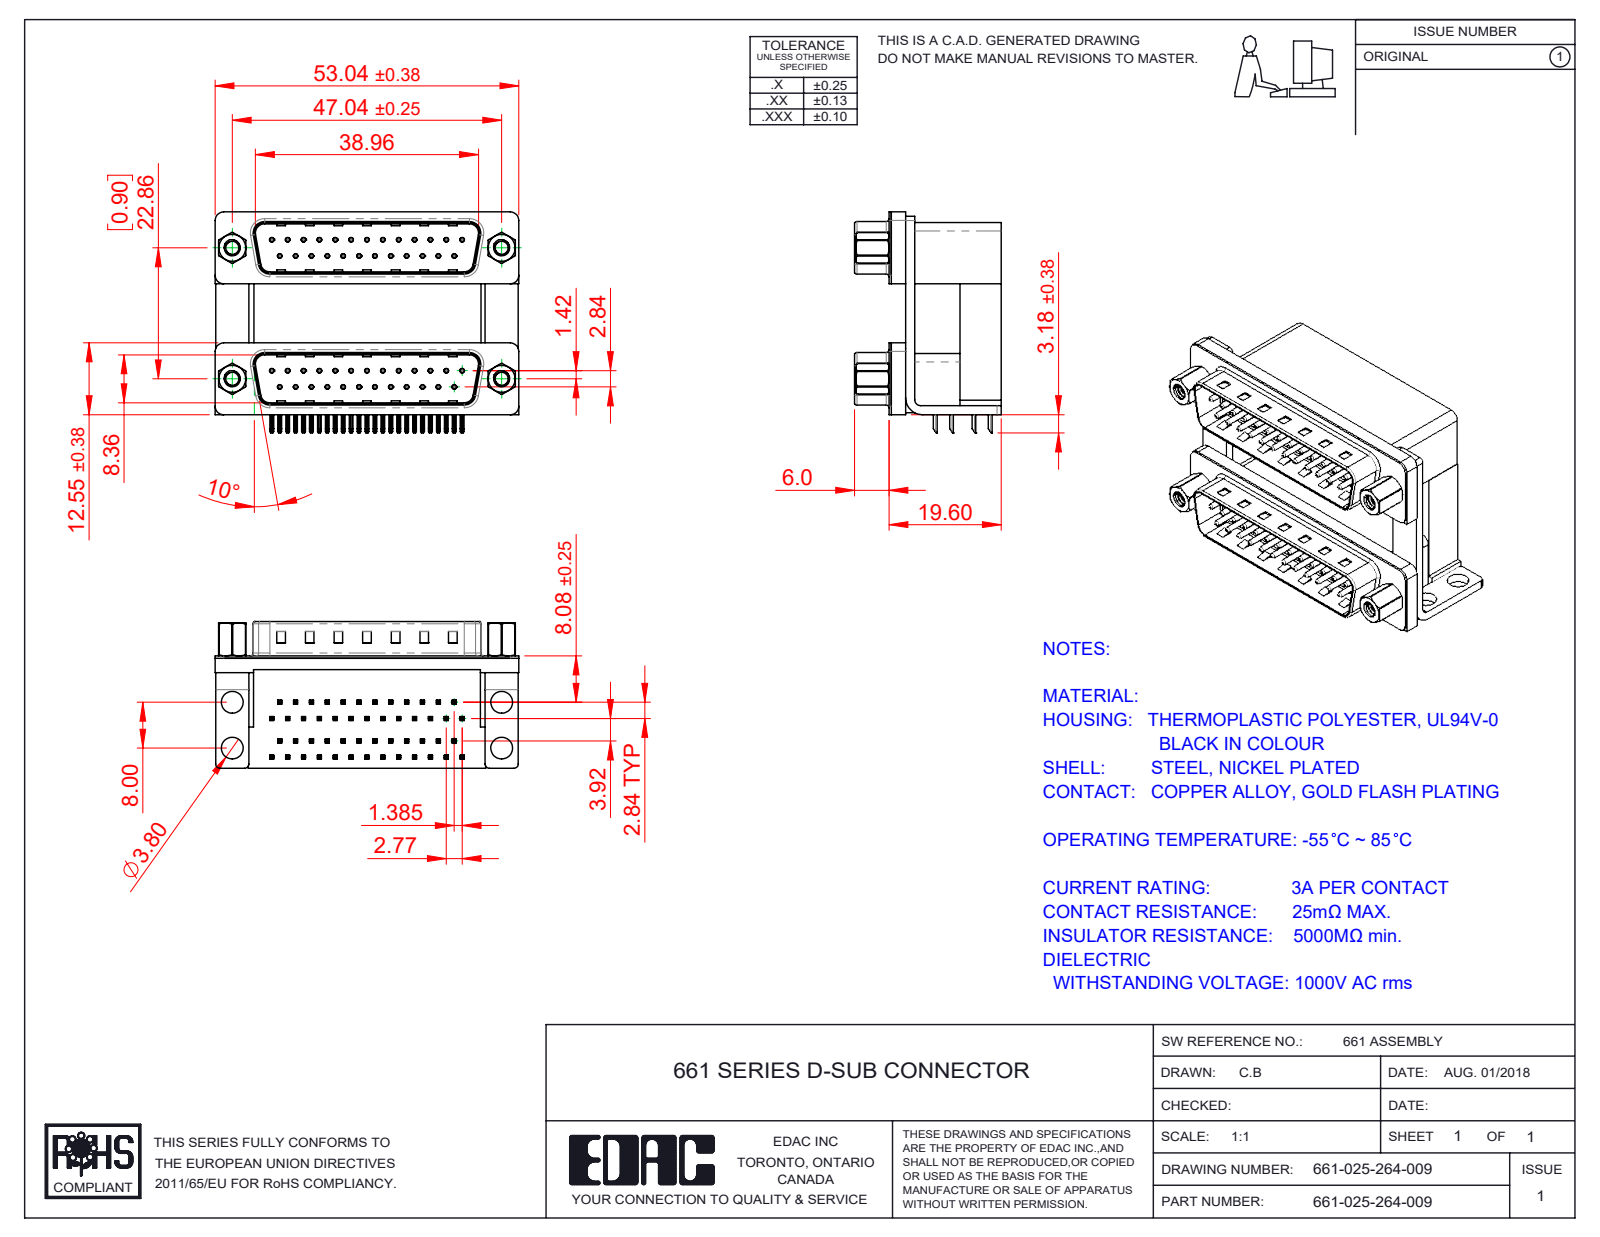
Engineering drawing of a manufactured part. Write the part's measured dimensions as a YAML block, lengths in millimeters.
part_name: "661 Mounting Bracket_NoneH; 661 Contact Top Upper_H; 661 4-40 Hex Standoff 5; 661 Housing Lower_25 Contacts (+8 more)"
step_written_by: "SolidWorks 2020 (CONFIG_CONTROL_DESIGN)"
units: millimeters
bodies: {solids: 65, faces: 4846, planar: 2978, cylindrical: 1410, other: 458}
overall_size: [53.04, 38.59, 25.6]
volume: 22579
surface_area: 23661
round_holes:
  - {diameter: 0.35, count: 50}
  - {diameter: 0.8, count: 50}
  - {diameter: 2.26, count: 4}
  - {diameter: 2.29, count: 4}
  - {diameter: 3.5, count: 4}
  - {diameter: 4, count: 4}
  - {diameter: 4.8, count: 4}
  - {diameter: 5, count: 4}
round_bosses_or_shafts:
  - {diameter: 0.75, count: 50}
  - {diameter: 4.9, count: 4}
  - {diameter: 4.75, count: 4}
  - {diameter: 3.9, count: 4}
  - {diameter: 2.79, count: 4}
partial_cylinders:
  - {radius: 0.25, count: 200}
  - {radius: 0.12, count: 100}
  - {radius: 0.5, count: 16}
  - {radius: 1.5, count: 14}
  - {radius: 0.9, count: 8}
  - {radius: 1.6, count: 8}
  - {radius: 2, count: 8}
  - {radius: 0.4, count: 4}
face_to_face_distances: [12, 0.4, 19.2, 22.86, 7.2, 12.4, 16.7, 9.5, 2.5, 10.7]
hole_center_spacings: [2.77, 3.16, 5.54, 8.31, 11.08, 13.85, 16.62, 5.03]
